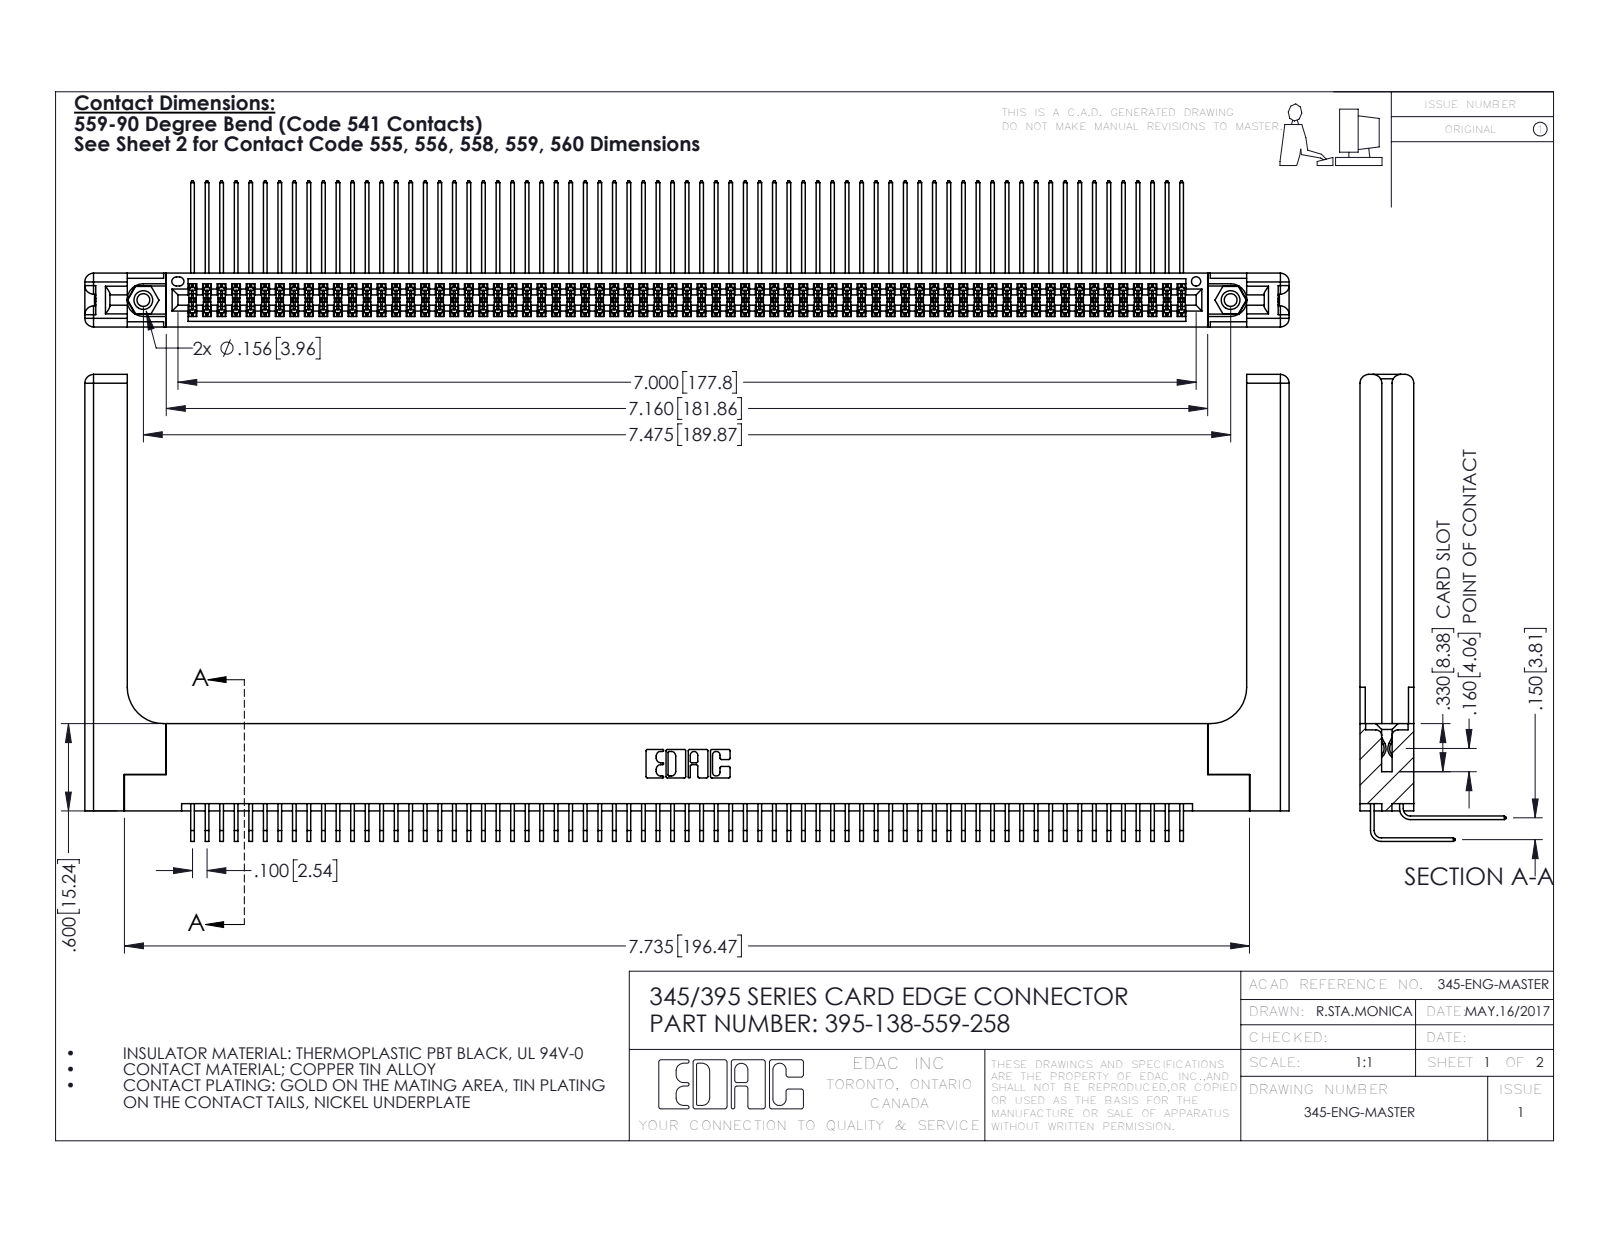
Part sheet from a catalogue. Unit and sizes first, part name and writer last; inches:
Units: inches
Overall size (bounding box): 8.279 × 3.209 × 1.005
Round holes (diameter × count): ⌀0.089 ×2, ⌀0.125 ×2, ⌀0.156 ×2, ⌀0.064 ×1
Round bosses / shafts (diameter × count): ⌀0.155 ×2
Partial cylindrical surfaces — rounded edges, fillets, slot ends (radius × count): R0.006 ×275, R0.01 ×22, R0.06 ×16, R0.007 ×6, R0.031 ×6, R0.026 ×3, R0.014 ×2, R0.019 ×2
Main face-to-face distances: 0.072, 0.298, 0.37, 0.2, 0.098, 0.272, 0.025, 0.225, 0.175, 0.15
Hole centre spacings: 0.27, 7.239, 7.475
Volume: 1.828 in³ · Surface area: 63.66 in²
Bodies: 143 solids, 7558 faces (5058 planar, 2440 cylindrical, 60 other)
Part name (STEP PRODUCT): 345-250-001_345-250-001-102; 395-138-559-258; 345-292-001_559 Tail - 2; 345-220-058_345-220-058 (+2 more)
STEP written by: SolidWorks 2016 (CONFIG_CONTROL_DESIGN)
